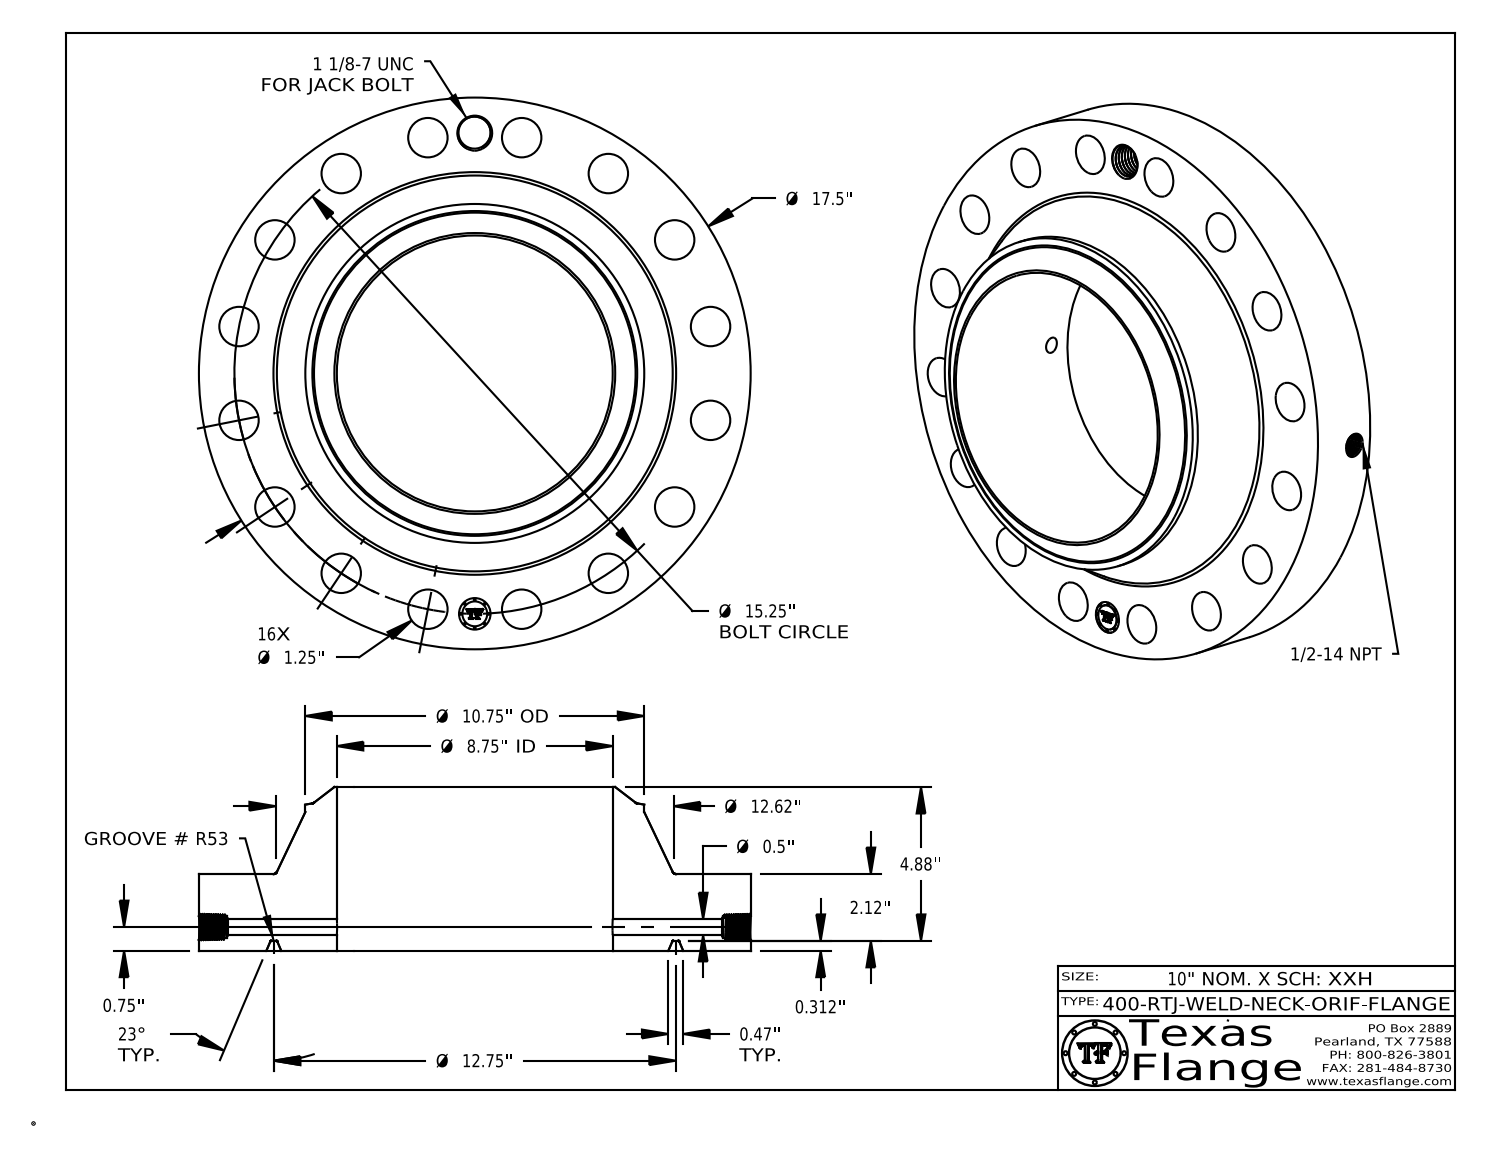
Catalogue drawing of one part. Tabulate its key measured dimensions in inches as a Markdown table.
| quantity | value |
| --- | --- |
| part name | 400-RTJ-WELD-NECK |
| STEP written by | CATIA V5 STEP AP214 (AUTOMOTIVE_DESIGN) |
| units | inches |
| bodies | 1 solid, 810 faces (370 planar, 112 cylindrical, 328 other) |
| overall size | 17.5 × 17.5 × 5.192 |
| volume | 490.2 in³ |
| surface area | 852 in² |
| round holes (diameter × count) | 1.25 × 16, 0.5 × 1, 0.672 × 1, 0.984 × 1, 1 × 1, 8.75 × 1 |
| round bosses / shafts (diameter × count) | 0.061 × 8, 17.5 × 1, 10.75 × 1, 0.788 × 1 |
| main face-to-face distances | 2.432, 0.312, 2.12, 5.192, 4.88, 2.76, 0.015, 2.417, 2.105, 2.775 |
| hole center spacings | 5.836, 7.625, 10.783, 14.089, 14.957, 2.975, 2.975, 8.472 |
